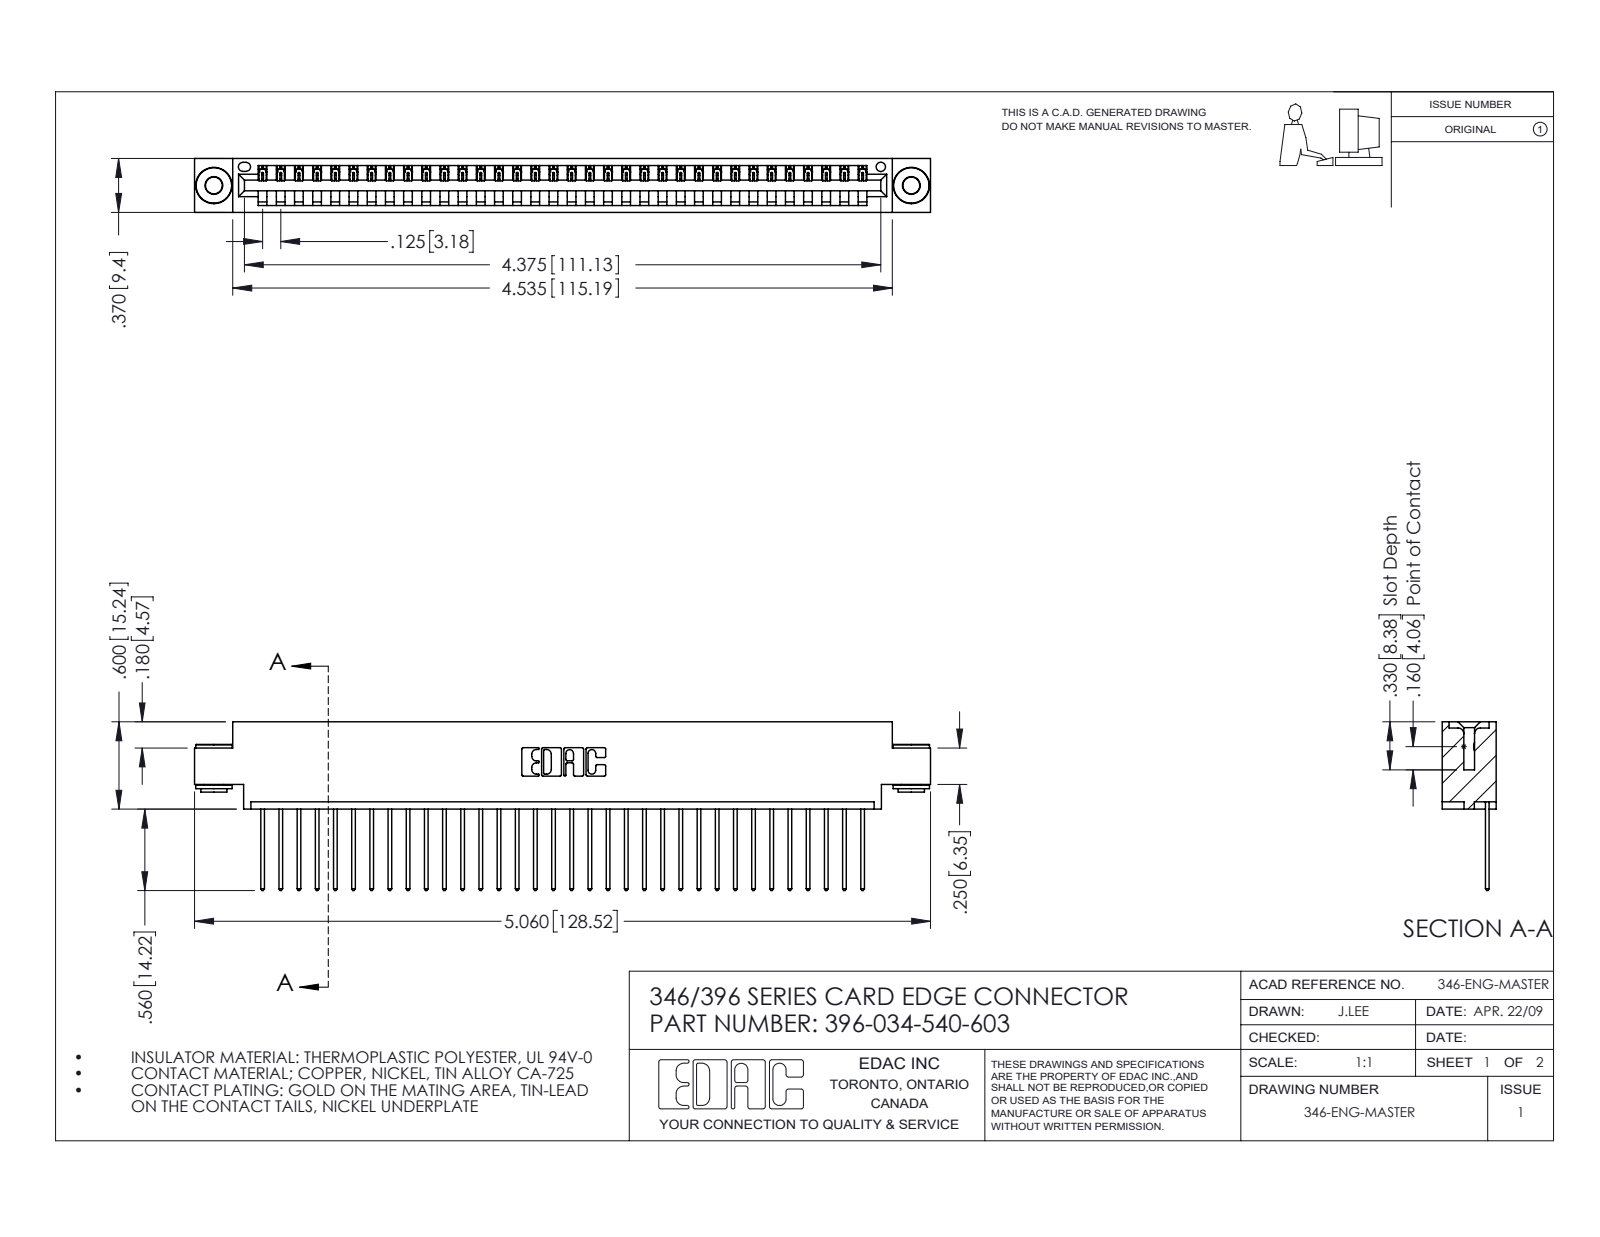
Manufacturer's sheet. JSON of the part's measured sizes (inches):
{"part_name": "345-292-001_345-293-140; 396-034-540-603; 346 Part_0.170 Offset - 0.156 Dia-TH; 345-250-002_345-250-002-102", "step_written_by": "SolidWorks 2016 (CONFIG_CONTROL_DESIGN)", "units": "inches", "bodies": {"solids": 37, "faces": 2136, "planar": 1450, "cylindrical": 678, "other": 8}, "overall_size": [5.06, 1.16, 0.37], "volume_in3": 0.742, "surface_area_in2": 24.53, "round_holes": [[0.116, 2], [0.156, 2], [0.064, 1]], "round_bosses_or_shafts": [[0.25, 2], [0.18, 2], [0.136, 2]], "partial_cylinders_radius": [[0.006, 68], [0.01, 68], [0.01, 22], [0.007, 6], [0.031, 6], [0.026, 3], [0.031, 2], [0.04, 2]], "face_to_face_distances": [0.048, 0.322, 0.37, 0.25, 0.025, 0.072, 0.298, 0.148, 0.222, 0.1], "hole_center_spacings": [0.246, 4.587, 4.795]}
